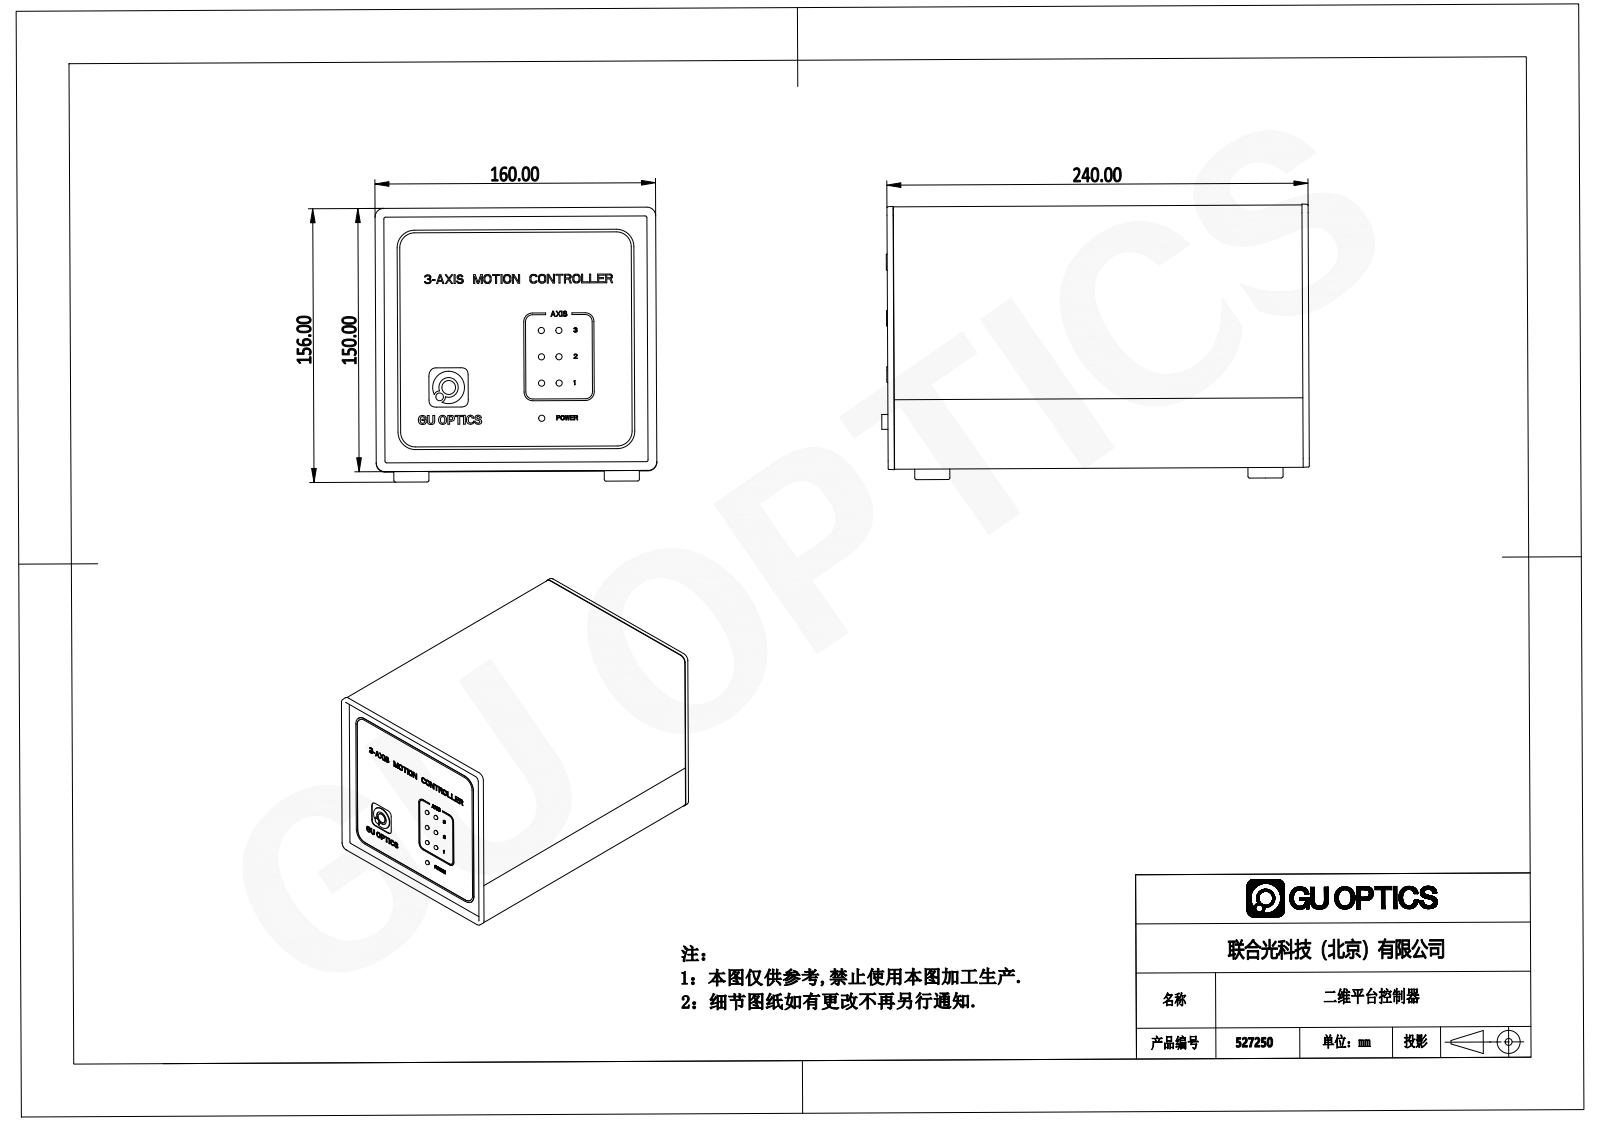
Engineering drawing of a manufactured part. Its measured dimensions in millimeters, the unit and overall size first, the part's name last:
Units: millimetres
Overall size (bounding box): 243.65 × 160 × 156
Round holes (diameter × count): ⌀2.5 ×18, ⌀3.5 ×11, ⌀4.5 ×6, ⌀3.2 ×4, ⌀7 ×4, ⌀7.15 ×4, ⌀1.5 ×2, ⌀2 ×1, ⌀5.7 ×1, ⌀11.5 ×1
Round bosses / shafts (diameter × count): ⌀1.09 ×69, ⌀1 ×45, ⌀20 ×4, ⌀0.92 ×4, ⌀1.2 ×2, ⌀12.5 ×1, ⌀8 ×1, ⌀2 ×1
Partial cylindrical surfaces — rounded edges, fillets, slot ends (radius × count): R1 ×58, R1.5 ×36, R1.8 ×36, R2 ×36, R0.5 ×32, R0.4 ×30, R2.5 ×24, R3 ×18
Main face-to-face distances: 1, 148.5, 158.5, 2, 229.15, 149.5, 147.5, 157.5, 159.5, 231.15
Hole centre spacings: 32, 40.61, 51.62, 64, 25, 40.5, 15, 18.03
Volume: 311 543 mm³ · Surface area: 438 099 mm²
Bodies: 28 solids, 3048 faces (2144 planar, 575 cylindrical, 329 other)
Part name (STEP PRODUCT): dzqkx160-150-2501
STEP written by: SolidWorks 2020 (CONFIG_CONTROL_DESIGN)
